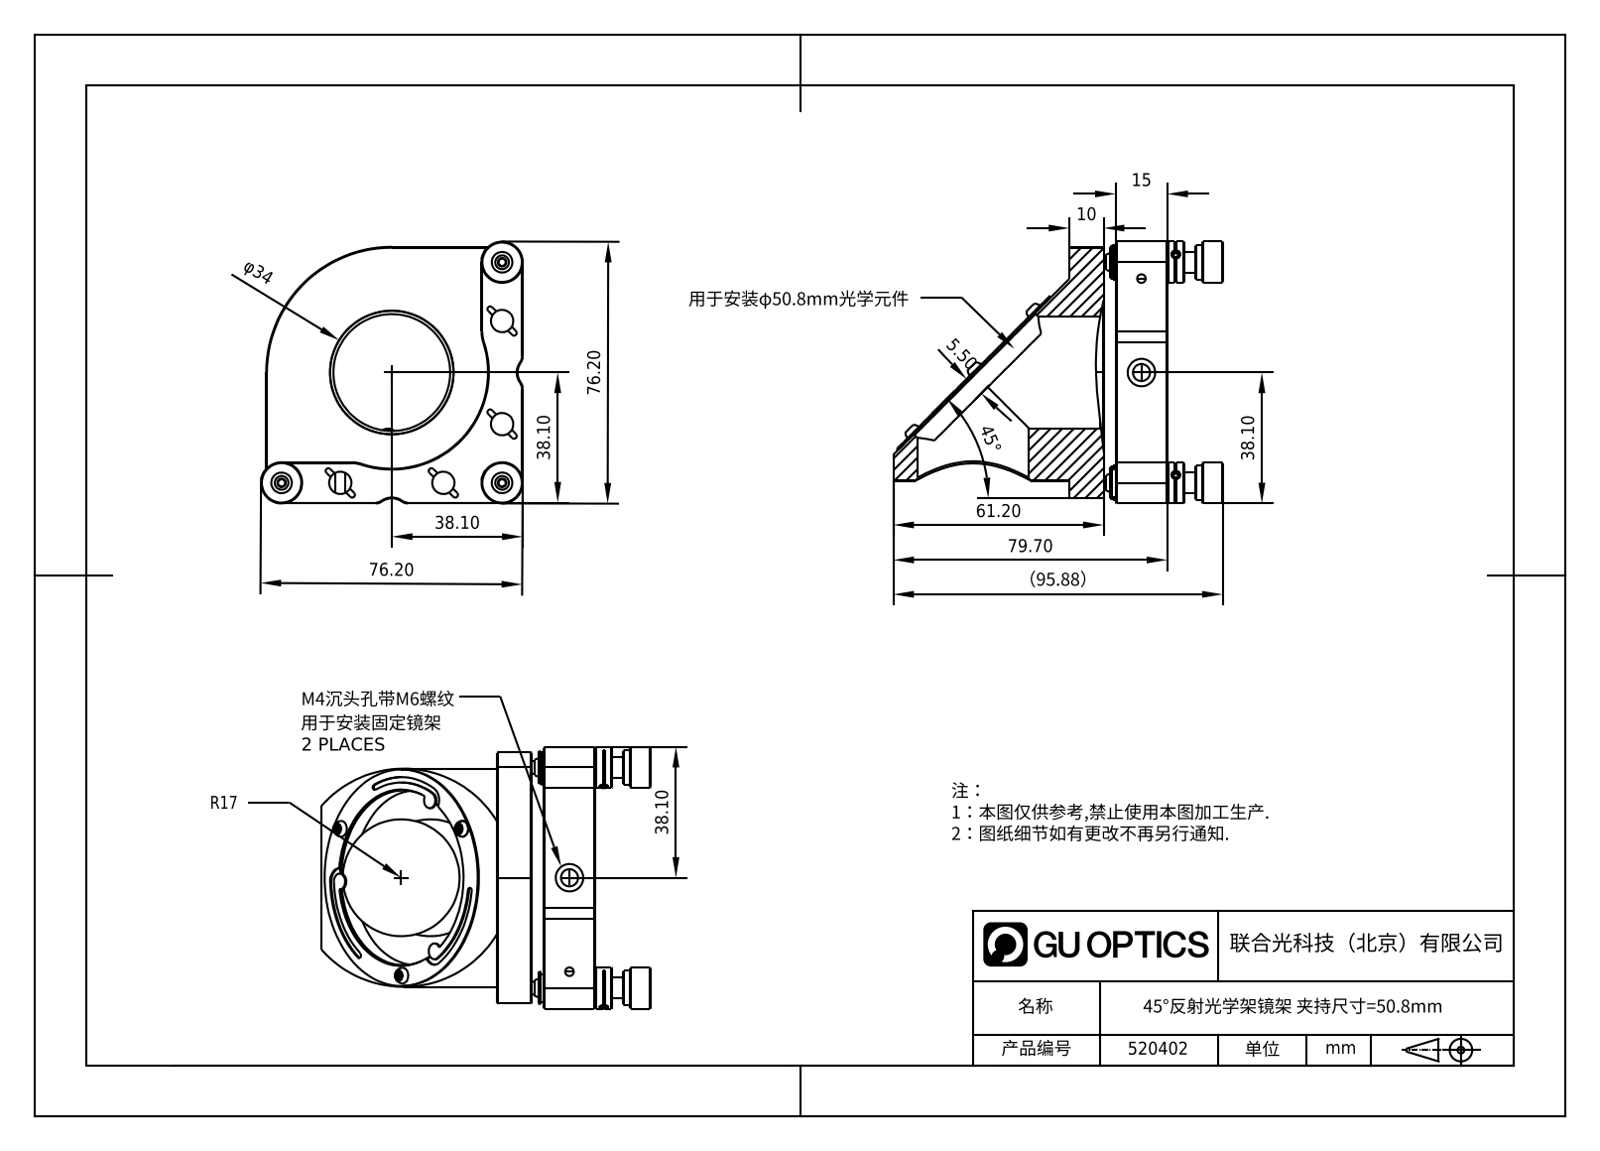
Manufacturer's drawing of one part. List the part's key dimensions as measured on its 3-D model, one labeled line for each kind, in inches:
Part name (STEP PRODUCT): 520402
STEP written by: SolidWorks 2020 (AUTOMOTIVE_DESIGN)
Units: inches
Bodies: 0 solids, 355 faces (154 planar, 101 cylindrical, 100 other)
Overall size (bounding box): 3.775 × 3.001 × 3
Round holes (diameter × count): ⌀0.098 ×6, ⌀0.315 ×5, ⌀0.256 ×4, ⌀0.157 ×3, ⌀0.374 ×3, ⌀0.081 ×2, ⌀0.106 ×2, ⌀0.197 ×2, ⌀1.339 ×2, ⌀2 ×1, ⌀2.02 ×1
Round bosses / shafts (diameter × count): ⌀0.472 ×3, ⌀0.394 ×3, ⌀0.236 ×3, ⌀0.118 ×2, ⌀0.059 ×2, ⌀2.5 ×1, ⌀2.48 ×1
Partial cylindrical surfaces — rounded edges, fillets, slot ends (radius × count): R0.031 ×11, R0.118 ×4, R0.091 ×3, R0.154 ×3, R0.177 ×3, R0.008 ×2, R0.197 ×2, R0.394 ×2
Main face-to-face distances: 0.394, 0.138, 0.531, 0.059, 0.591, 0.728, 1.122, 0.02, 0.236, 0.472
Hole centre spacings: 0.673, 1.122, 1.395, 1.854, 0.884, 1.077, 1.181, 1.787
